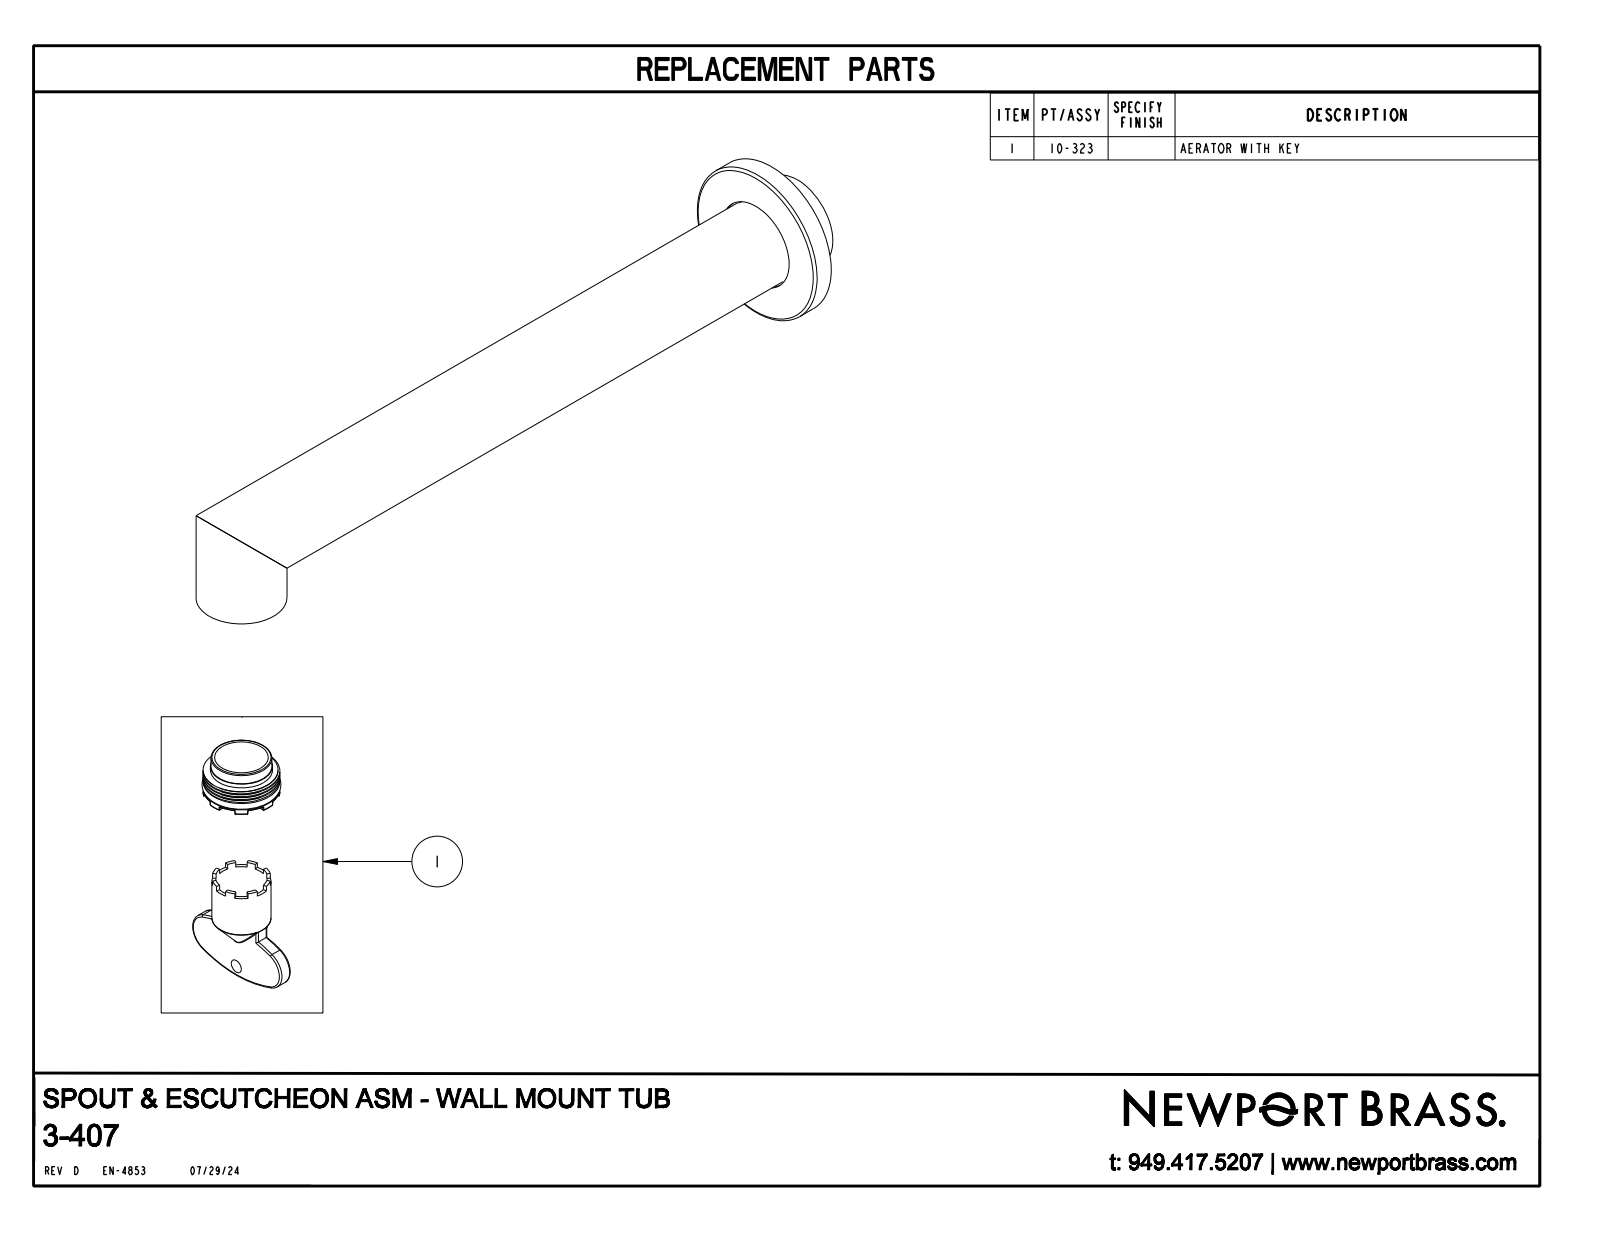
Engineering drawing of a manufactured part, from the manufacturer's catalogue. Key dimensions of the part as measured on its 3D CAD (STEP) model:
Part name (STEP PRODUCT): 3-407
STEP written by: CREO PARAMETRIC BY PTC INC, 2018400 (AUTOMOTIVE_DESIGN)
Units: inches
Bodies: 1 solid, 18 faces (6 planar, 8 cylindrical, 4 other)
Overall size (bounding box): 9.15 × 1.75 × 1.75
Volume: 7.853 in³ · Surface area: 35.59 in²
Round bosses / shafts (diameter × count): ⌀1 ×2, ⌀1.75 ×1, ⌀1.1 ×1
Main face-to-face distances: 0.25, 0.4, 0.65
